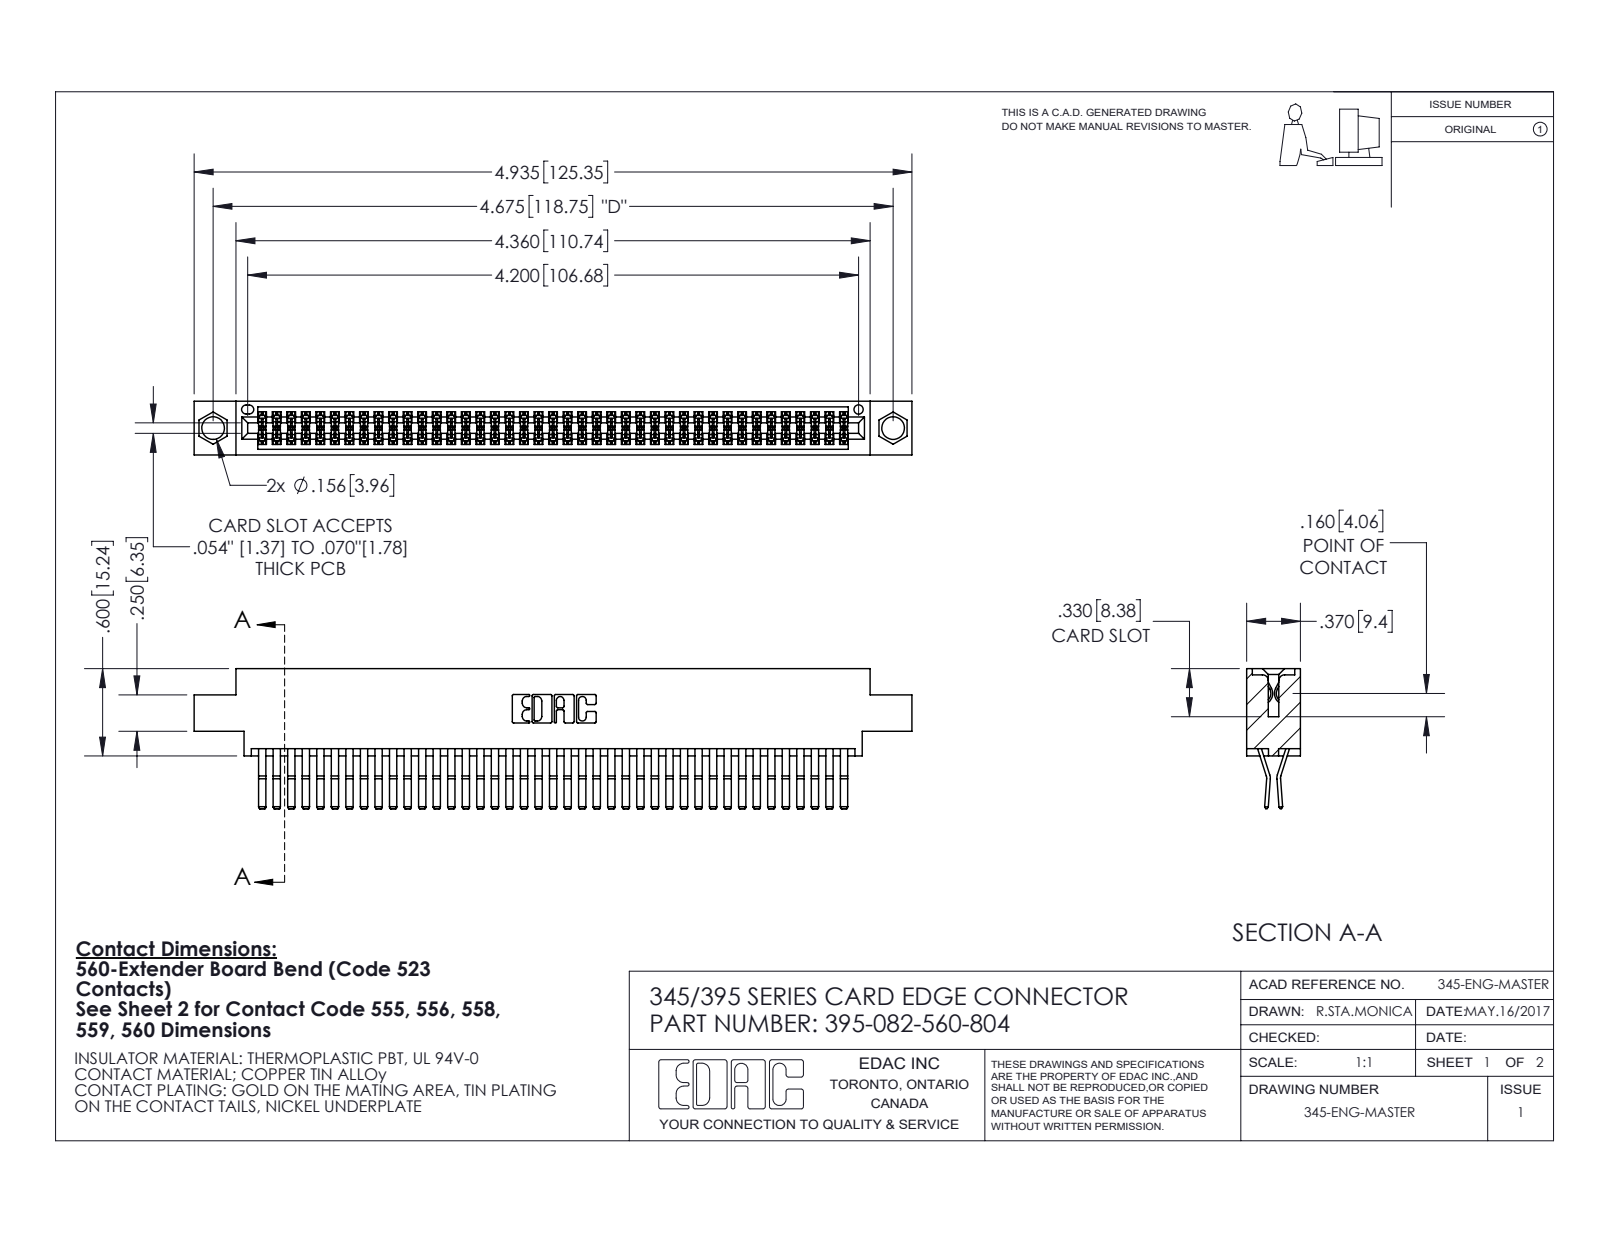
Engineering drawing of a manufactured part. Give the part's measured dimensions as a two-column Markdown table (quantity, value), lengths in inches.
| quantity | value |
| --- | --- |
| part name | 345 Part_0.170 Offset - 0.156 Dia-TI; 345-292-001_560 Tail; 395-082-560-804 |
| STEP written by | SolidWorks 2020 (CONFIG_CONTROL_DESIGN) |
| units | inches |
| bodies | 83 solids, 4408 faces (2804 planar, 1604 cylindrical, 0 other) |
| overall size | 4.935 × 0.962 × 0.37 |
| volume | 0.762 in³ |
| surface area | 30.71 in² |
| round holes (diameter × count) | 0.156 × 2, 0.064 × 1 |
| partial cylindrical surfaces (radius × count) | 0.006 × 123, 0.01 × 22, 0.007 × 6, 0.031 × 6, 0.026 × 3, 0.01 × 2, 0.014 × 2, 0.019 × 2 |
| main face-to-face distances | 0.025, 0.298, 0.072, 0.37, 0.2, 0.098, 0.272, 0.225, 0.175, 0.149 |
| hole center spacings | 0.27, 4.439, 4.675 |
